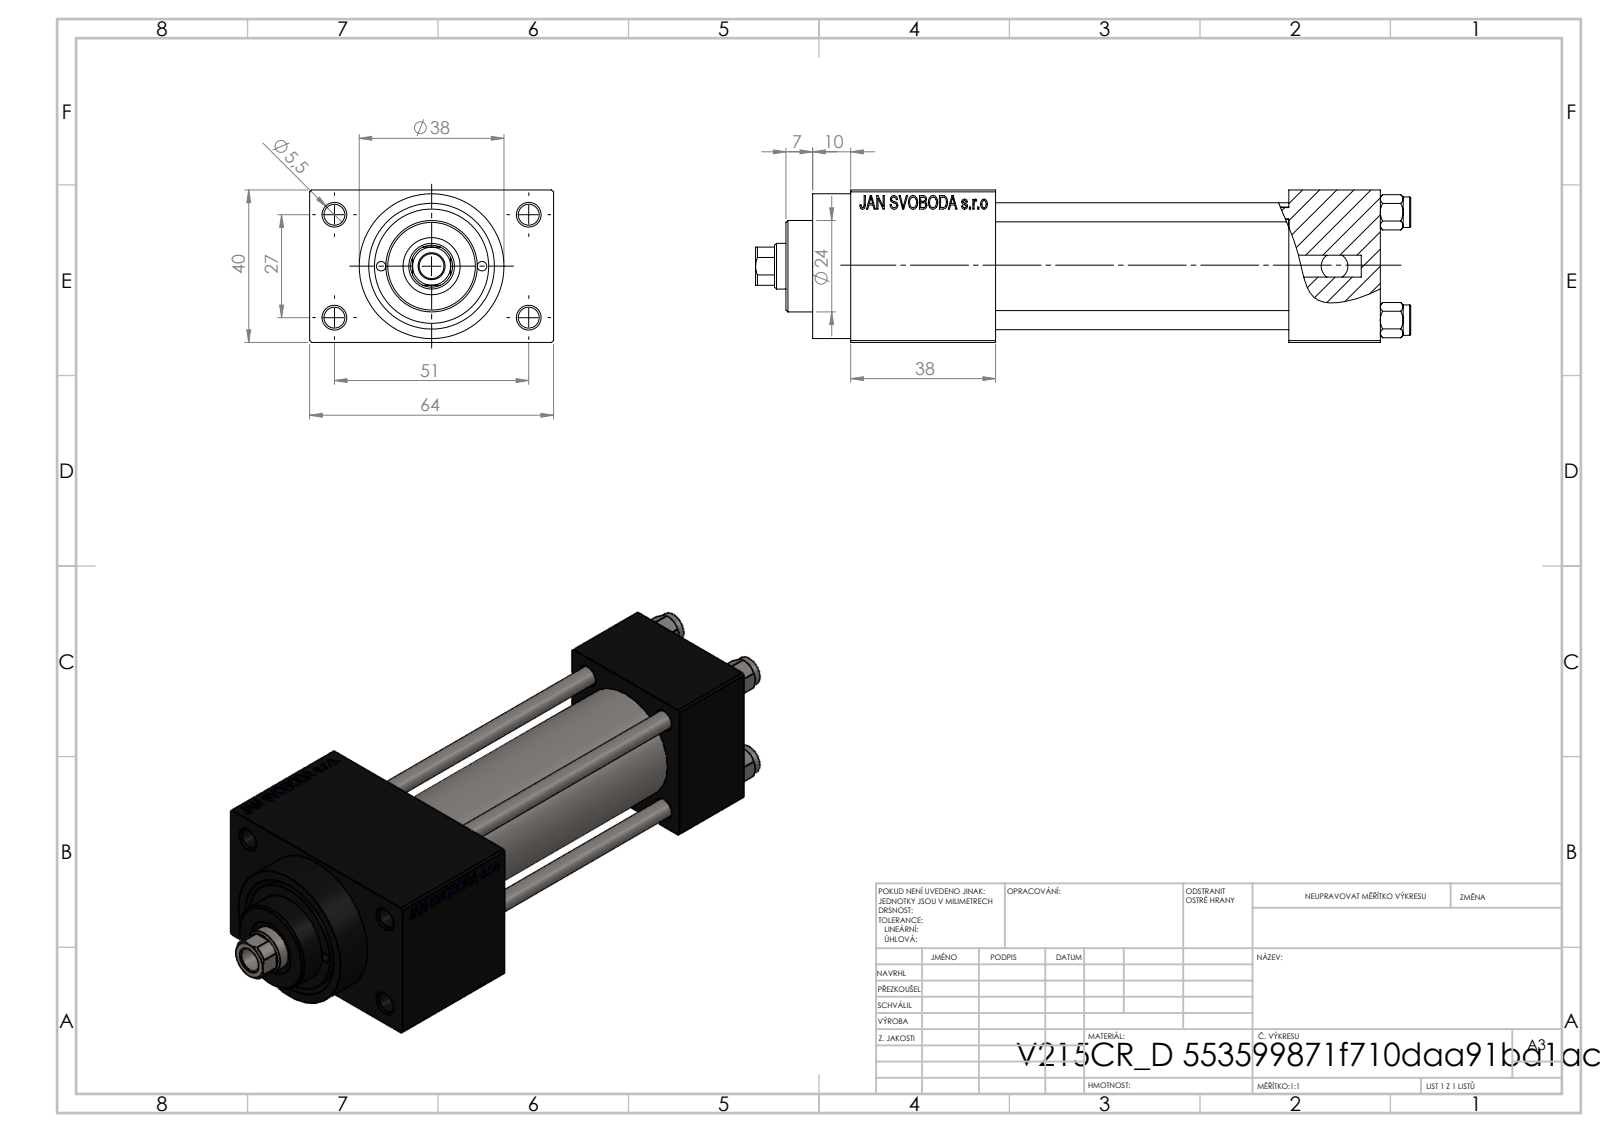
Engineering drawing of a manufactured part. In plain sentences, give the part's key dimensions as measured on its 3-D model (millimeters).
The part is named "V215CR_D_TYCINKA; V215_VC_A; V215CR_D_Body; V215CR_VCP_D (+1 more)". Its 3-D file was written by "SolidWorks 2019 (CONFIG_CONTROL_DESIGN)". It is 11 solids with 1110 faces: 498 planar, 92 cylindrical and 520 other. Overall it measures 172 by 64 by 40 millimeters. Its volume is 187 190 cubic millimeters and its surface area 70 452 square millimeters. Round holes: 4 of diameter 5, 4 of diameter 5.5, 3 of diameter 20, 2 of diameter 2.5, 2 of diameter 7, 2 of diameter 13.16, 1 of diameter 6.5, 1 of diameter 12, 1 of diameter 15, 1 of diameter 25, 1 of diameter 30. Round bosses or shafts: 4 of diameter 8, 1 of diameter 38, 1 of diameter 31, 1 of diameter 24. Partial cylindrical surfaces (rounded edges, fillets, slot ends): 1 of radius 5.5. The main face-to-face distances are 40, 12, 77, 24, 101, 52, 38, 139, 115, 64. The hole center spacings are 11.37, 14.18, 18.23, 20.01, 28.3, 28.85, 29.89, 30.84.
